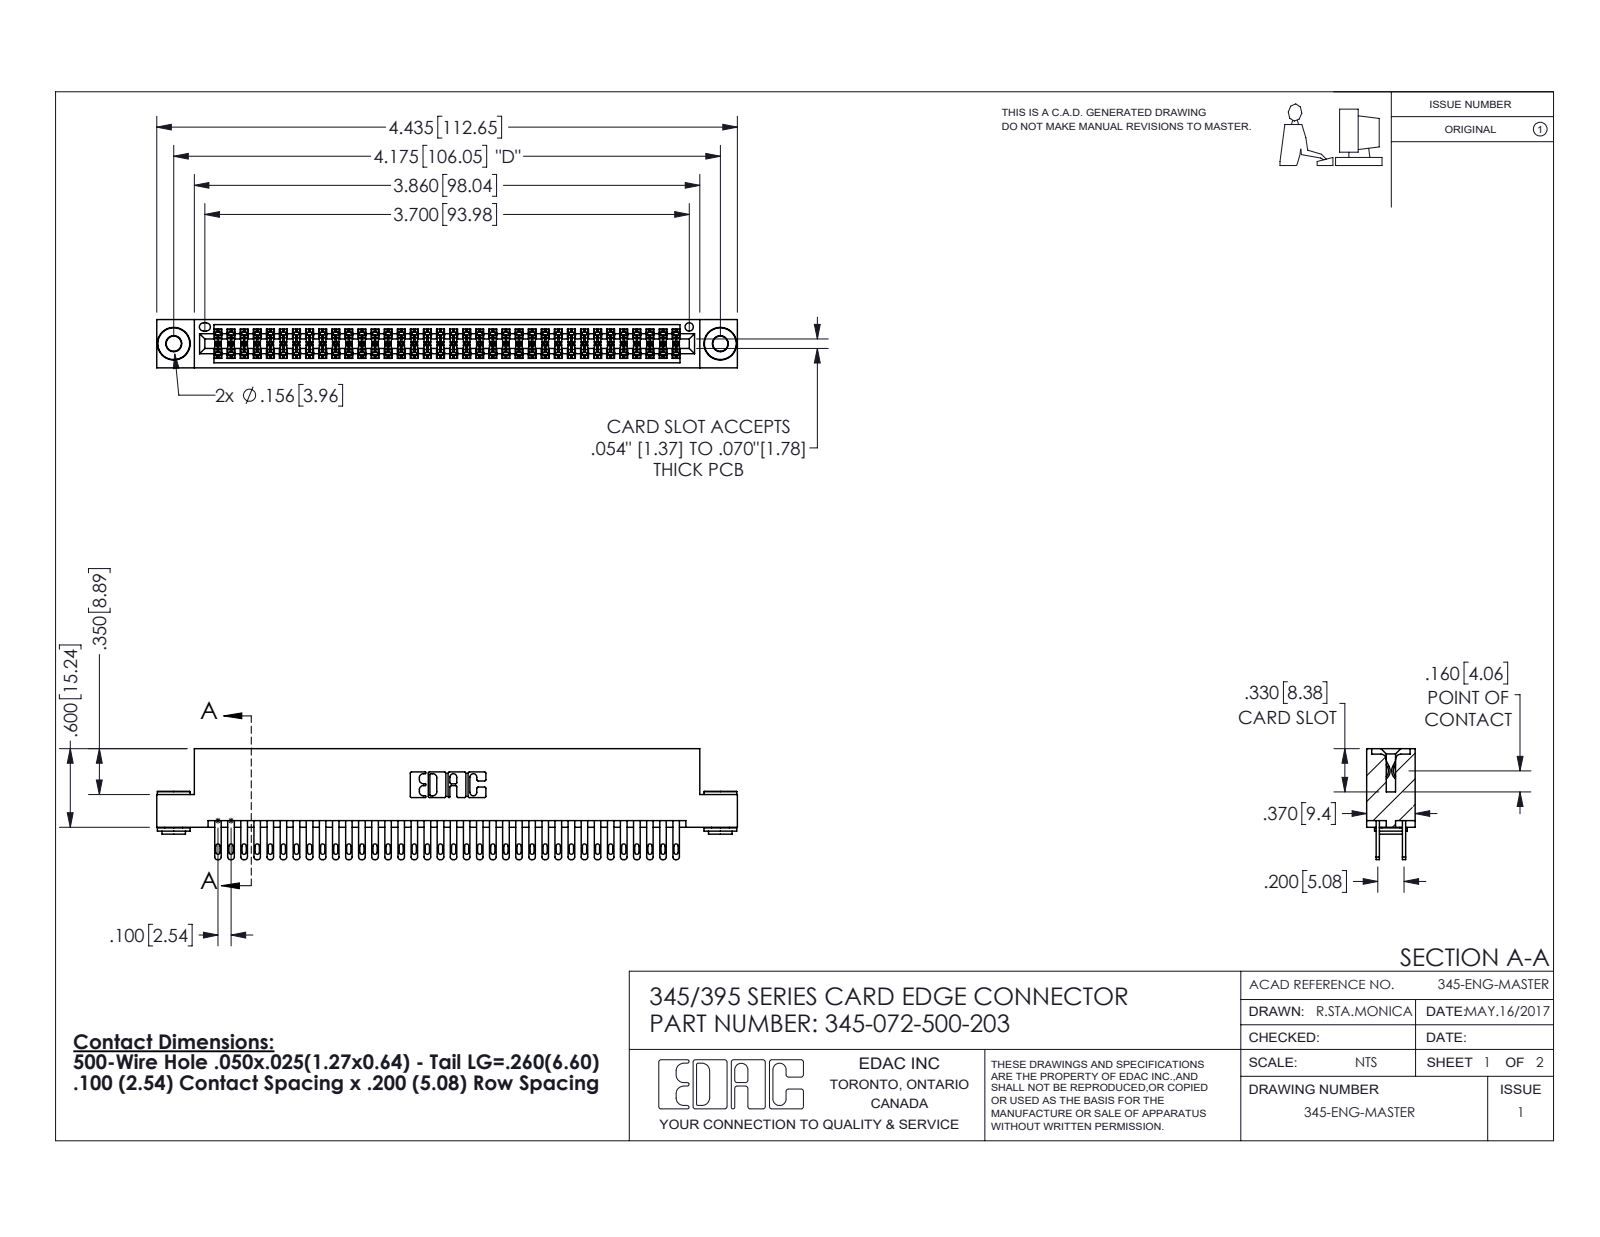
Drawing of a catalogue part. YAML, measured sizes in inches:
part_name: "345-250-002_345-250-002-102; 345-072-500-203; 345 Part_Flush Mounting Lugs - 0.156 Dia-TH; 345-292-001_345-293-100"
step_written_by: "SolidWorks 2016 (CONFIG_CONTROL_DESIGN)"
units: inches
bodies: {solids: 75, faces: 3476, planar: 2034, cylindrical: 1434, other: 8}
overall_size: [4.435, 0.847, 0.37]
volume: 0.679
surface_area: 26.77
round_holes:
  - {diameter: 0.116, count: 2}
  - {diameter: 0.156, count: 2}
  - {diameter: 0.064, count: 1}
round_bosses_or_shafts:
  - {diameter: 0.25, count: 2}
  - {diameter: 0.18, count: 2}
  - {diameter: 0.136, count: 2}
partial_cylinders:
  - {radius: 0.006, count: 108}
  - {radius: 0.016, count: 72}
  - {radius: 0.02, count: 72}
  - {radius: 0.01, count: 22}
  - {radius: 0.007, count: 6}
  - {radius: 0.031, count: 6}
  - {radius: 0.026, count: 3}
  - {radius: 0.014, count: 2}
face_to_face_distances: [0.072, 0.298, 0.2, 0.025, 0.098, 0.272, 0.37, 0.225, 0.175, 0.149]
hole_center_spacings: [0.27, 3.939, 4.175]
